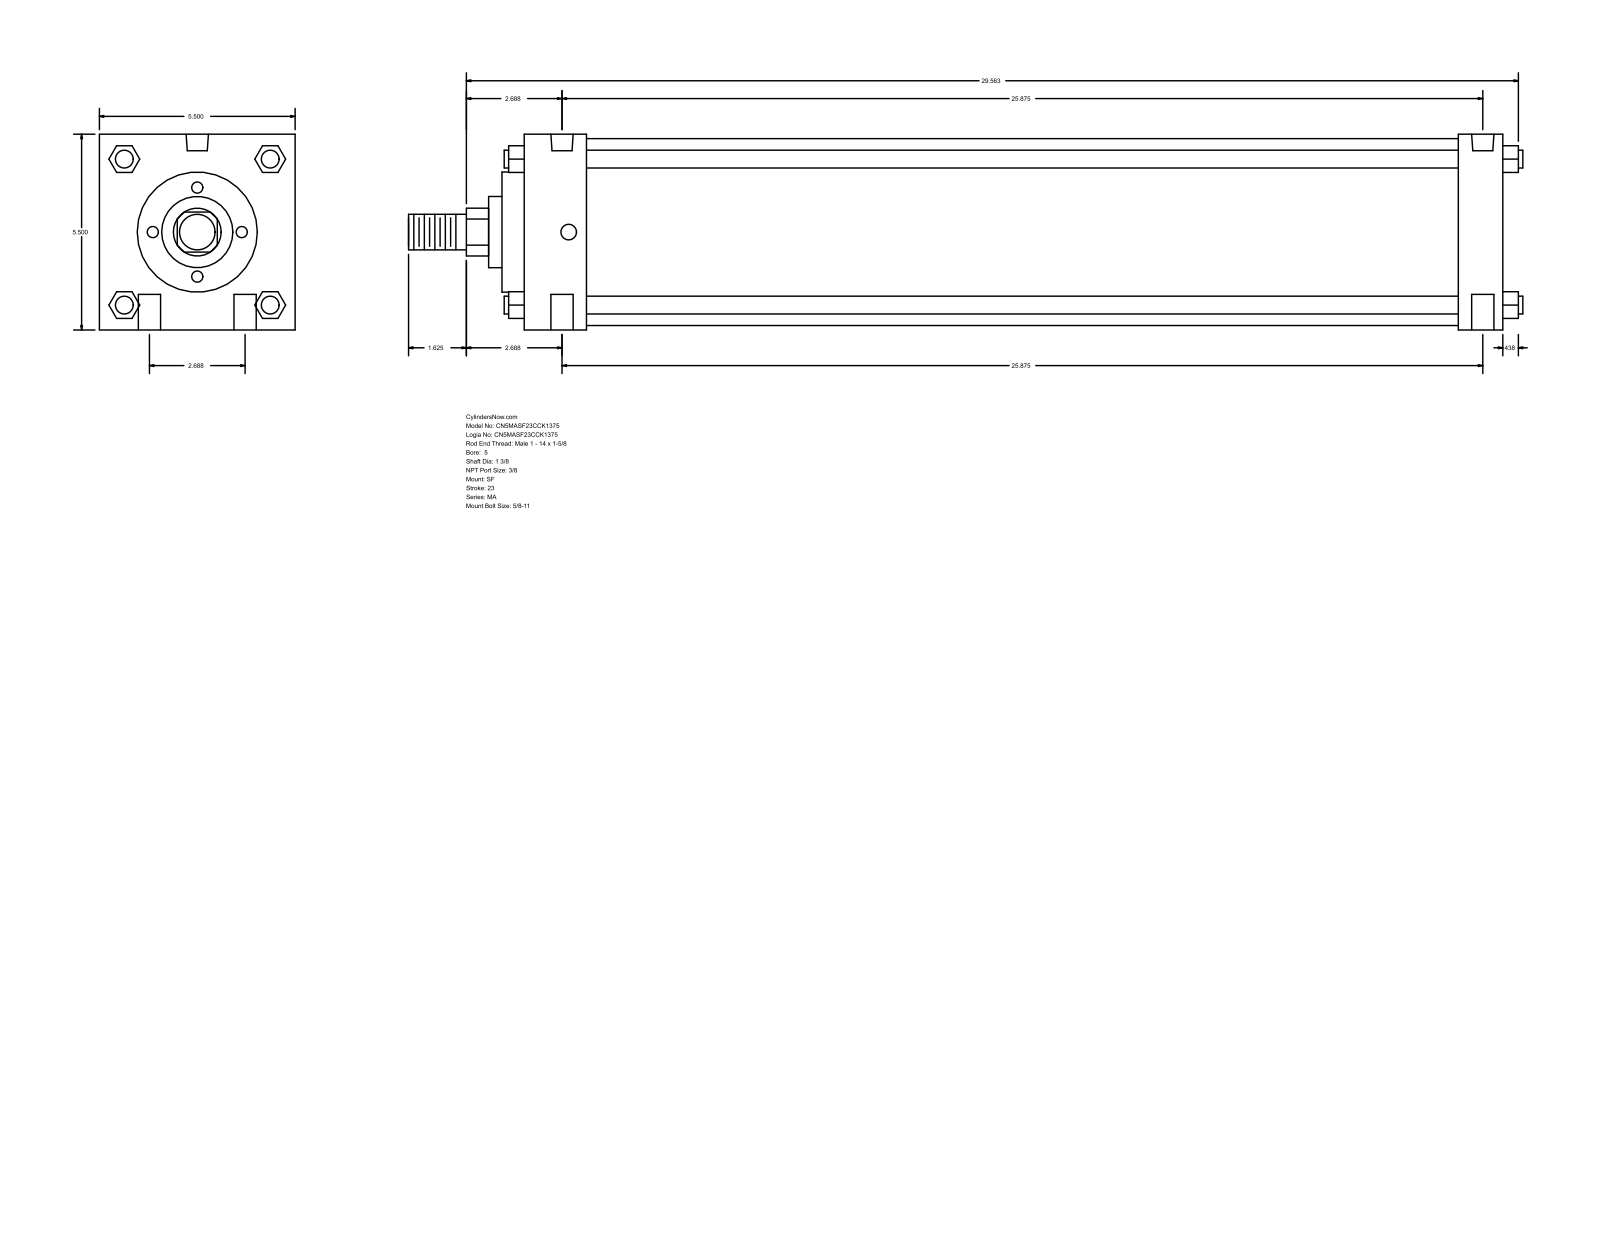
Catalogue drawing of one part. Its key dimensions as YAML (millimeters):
part_name: "MA_SF__0500_1.375"
step_written_by: "GSSL Pune (CONFIG_CONTROL_DESIGN)"
units: millimeters
bodies: {solids: 0, faces: 126, planar: 95, cylindrical: 31, other: 0}
overall_size: [795.34, 139.7, 139.7]
round_holes:
  - {diameter: 15.88, count: 4}
  - {diameter: 11.11, count: 2}
  - {diameter: 15.93, count: 2}
round_bosses_or_shafts:
  - {diameter: 12.7, count: 4}
  - {diameter: 133.35, count: 1}
  - {diameter: 85.72, count: 1}
  - {diameter: 50.8, count: 1}
  - {diameter: 34.92, count: 1}
  - {diameter: 25.4, count: 1}
partial_cylinders:
  - {radius: 17.06, count: 1}
face_to_face_distances: [139.7, 698.5, 44.45, 666.75, 622.3, 654.05, 31.75, 15.87, 60.32, 682.62]
hole_center_spacings: [34.13, 658.12, 657.23, 68.26, 660.77, 647.7]
